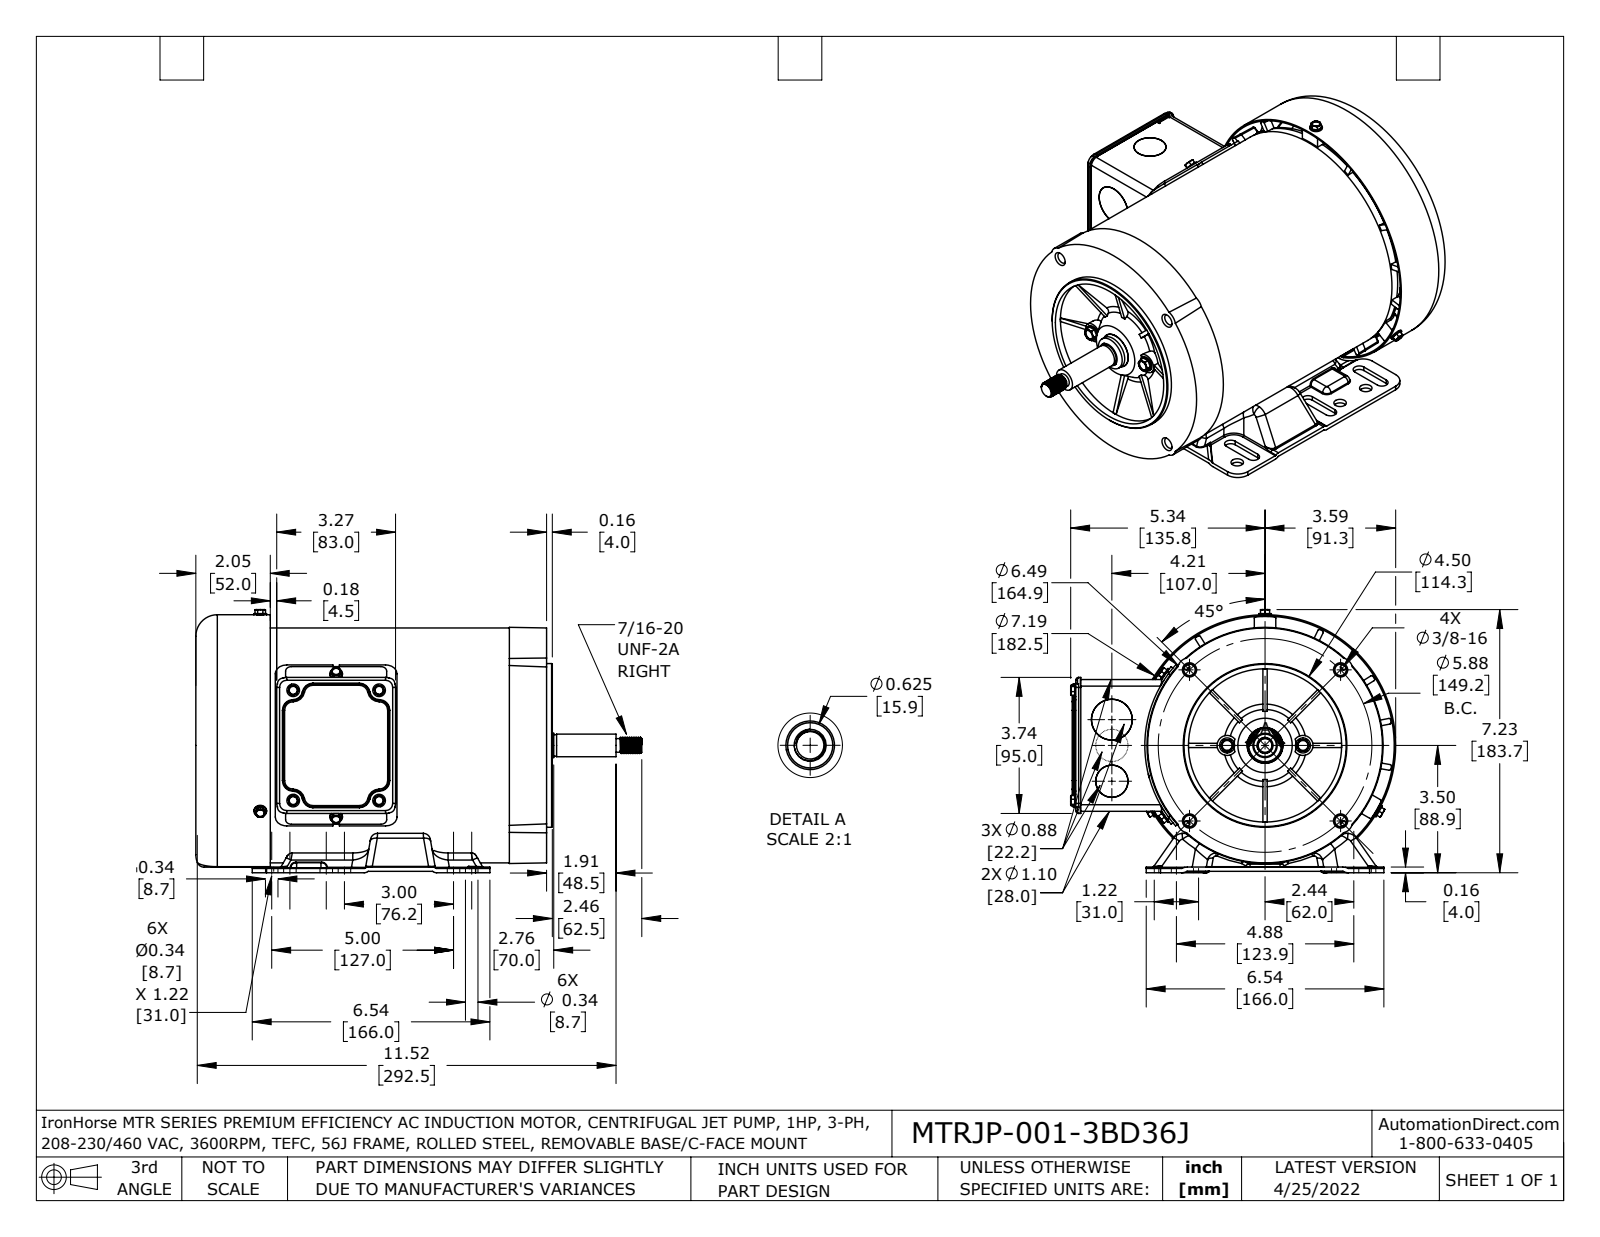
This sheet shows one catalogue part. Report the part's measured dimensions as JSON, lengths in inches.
{"part_name": "MTRJP-001-3BD36J redcmb1 coord fxt", "step_written_by": "SolidWorks 2021 (AUTOMOTIVE_DESIGN)", "units": "inches", "bodies": {"solids": 24, "faces": 2699, "planar": 648, "cylindrical": 879, "other": 1172}, "overall_size": [12.264, 8.938, 7.234], "volume_in3": 46.27, "surface_area_in2": 890.9, "round_holes": [[0.197, 10], [0.219, 9], [0.276, 8], [0.136, 7], [0.217, 6], [0.328, 6], [0.344, 6], [0.15, 4], [0.177, 4], [0.313, 4], [0.134, 2], [0.273, 2]], "round_bosses_or_shafts": [[0.164, 9], [0.348, 8], [0.236, 6], [0.414, 2], [0.19, 2], [7.185, 1], [4.5, 1], [0.945, 1]], "partial_cylinders_radius": [[0.118, 109], [0.039, 65], [0.157, 32], [0.02, 30], [0.138, 26], [0.079, 18], [0.276, 18], [0.172, 12]], "face_to_face_distances": [0.039, 0.118, 0.063, 0.157, 9.646, 9.606, 0.079, 3.559, 3.087, 0.047], "hole_center_spacings": [4.221, 3.031, 0.094, 2.32, 2.409, 2.937, 3.748, 3.841]}
